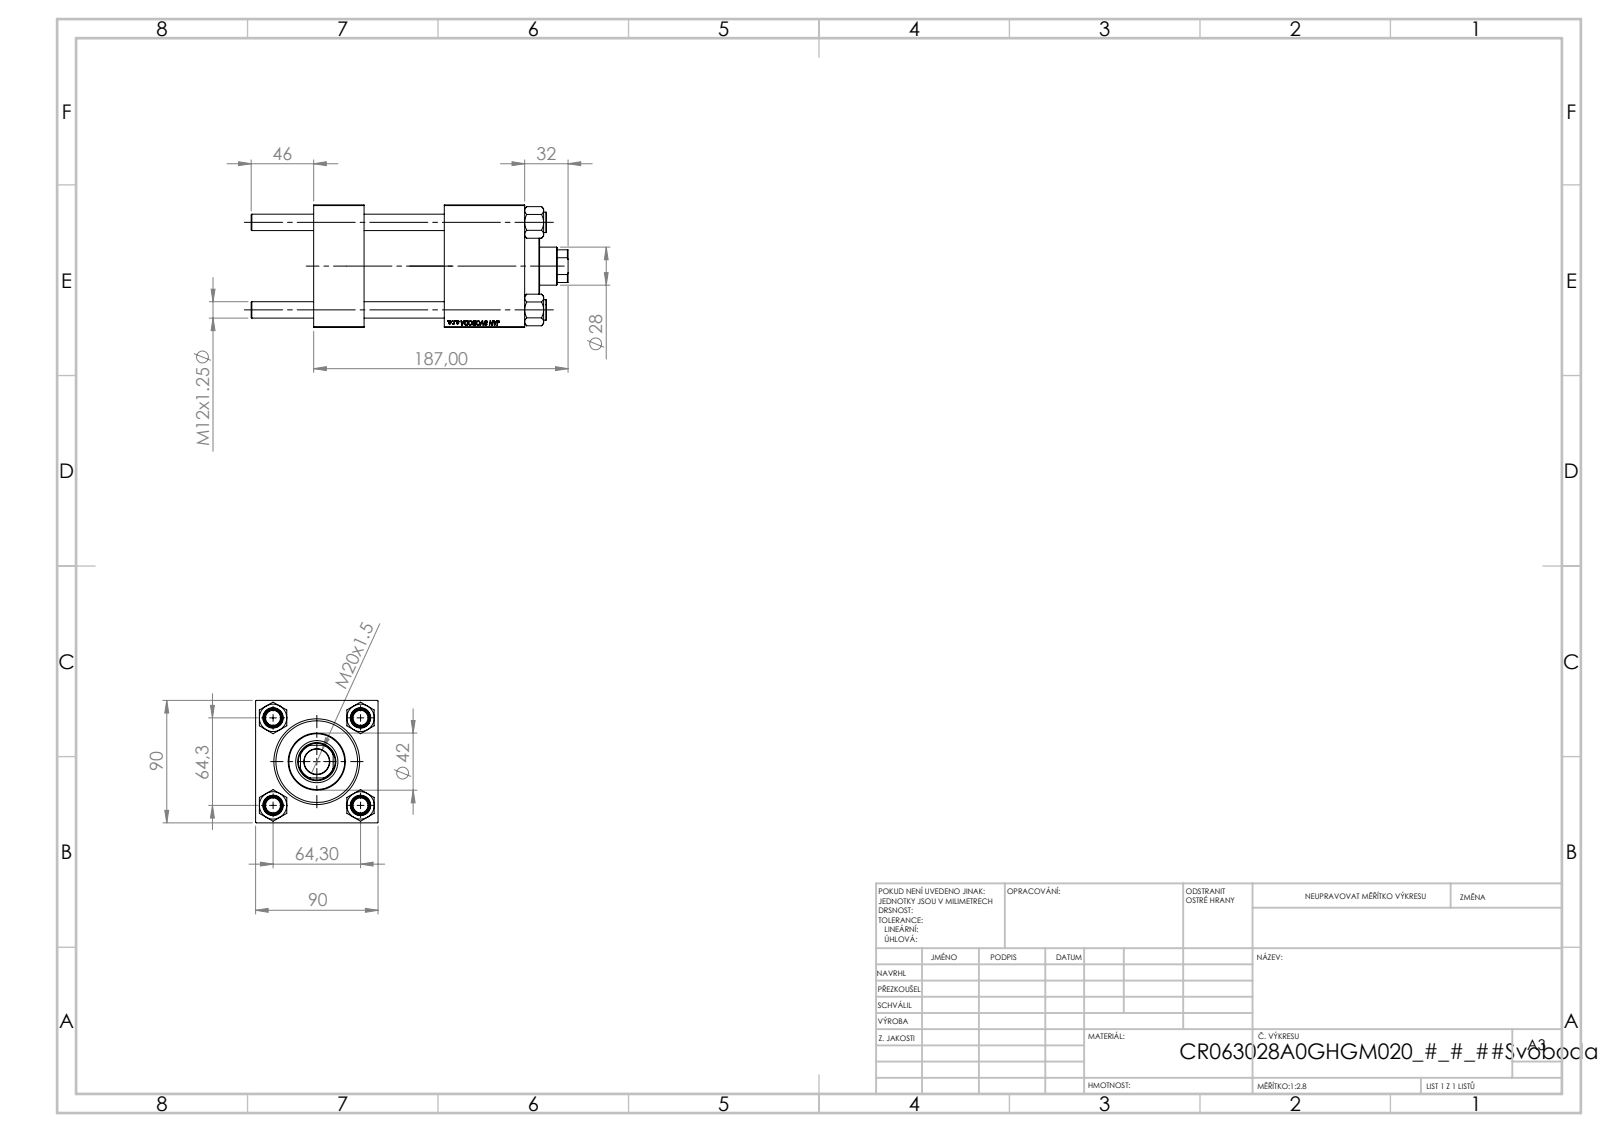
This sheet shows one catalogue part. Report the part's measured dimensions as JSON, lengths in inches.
{"part_name": "V215CR_BODY_A; CR025_012_A_0_G_A_G_M_020_+#_##_TYCINKA; NUT_M5; V215CR_VCP (+1 more)", "step_written_by": "SolidWorks 2019 (CONFIG_CONTROL_DESIGN)", "units": "inches", "bodies": {"solids": 11, "faces": 1134, "planar": 520, "cylindrical": 78, "other": 536}, "overall_size": [9.173, 3.543, 3.543], "volume_in3": 59.88, "surface_area_in2": 302.7, "round_holes": [[0.472, 4], [0.276, 2], [0.825, 2], [1.181, 2], [0.728, 1], [1.102, 1], [1.22, 1], [1.969, 1], [2.362, 1], [2.48, 1]], "round_bosses_or_shafts": [[0.591, 4], [2.717, 1], [1.654, 1]], "partial_cylinders_radius": [[0.531, 1]], "face_to_face_distances": [3.543, 2.323, 1.457, 6.102, 4.646, 3.78, 4.972, 3.516, 1.193, 1.13], "hole_center_spacings": [1.79, 2.531, 3.58, 3.839]}
